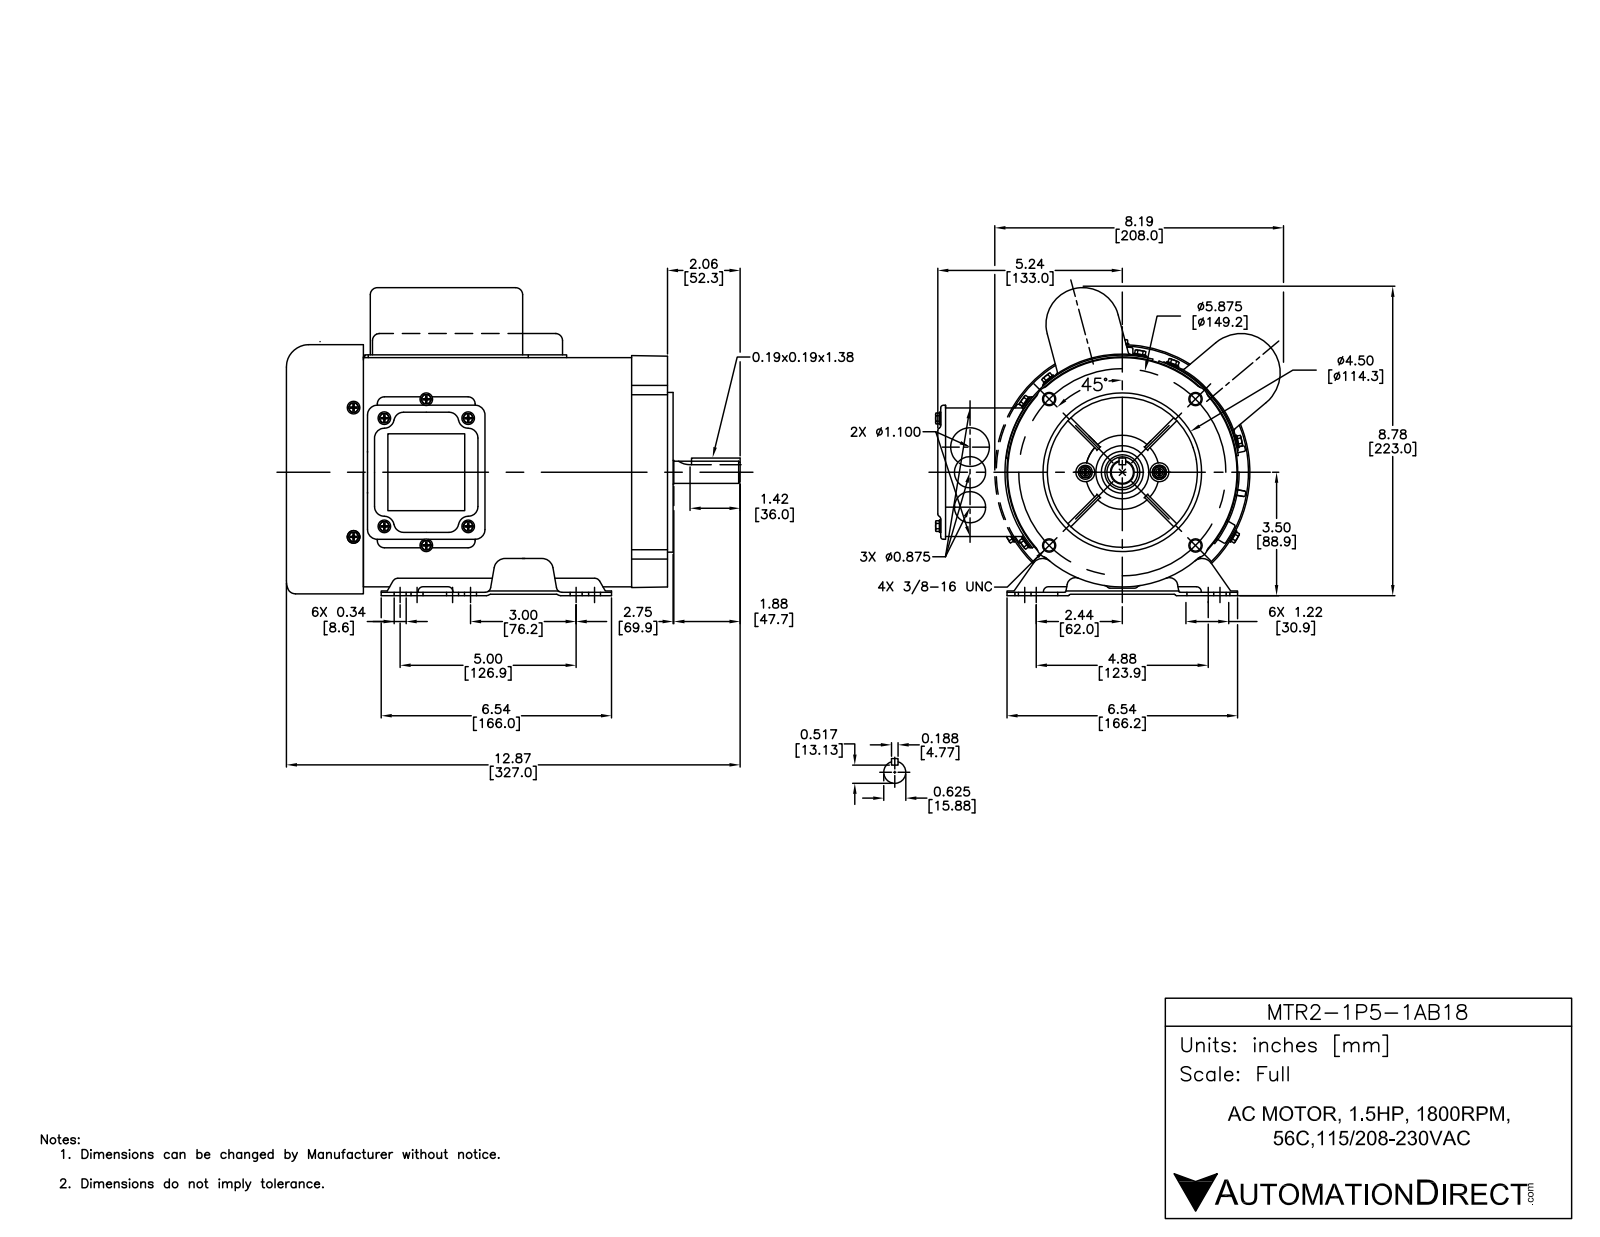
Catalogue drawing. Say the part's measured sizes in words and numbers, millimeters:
The part is named "MTR2-1P5-1AB18". Its 3-D file was written by "SolidWorks 2015 (AUTOMOTIVE_DESIGN)". It is 0 solids with 1388 faces: 535 planar, 576 cylindrical and 277 other. Overall it measures 326.97 by 238.97 by 227.73 millimeters. Round holes: 11 of diameter 5.56, 6 of diameter 6.3, 6 of diameter 8.73, 5 of diameter 7, 4 of diameter 7.94, 2 of diameter 5.5, 2 of diameter 6.93, 2 of diameter 13, 1 of diameter 3.15, 1 of diameter 8, 1 of diameter 29, 1 of diameter 107. Round bosses or shafts: 13 of diameter 8.84, 2 of diameter 14, 2 of diameter 10.52, 2 of diameter 4.17, 1 of diameter 182.5, 1 of diameter 165, 1 of diameter 162.5, 1 of diameter 114.3. Partial cylindrical surfaces (rounded edges, fillets, slot ends): 97 of radius 3, 32 of radius 1, 23 of radius 1.91, 16 of radius 2.54, 16 of radius 7, 14 of radius 5, 14 of radius 5.8, 13 of radius 3.05. The main face-to-face distances are 1, 35.25, 34.25, 274.65, 273.65, 239.4, 1.9, 3.1, 32.15, 31.15. The hole center spacings are 77, 58.94, 74.61, 95.21, 139.7, 25.4, 26.5, 60.
